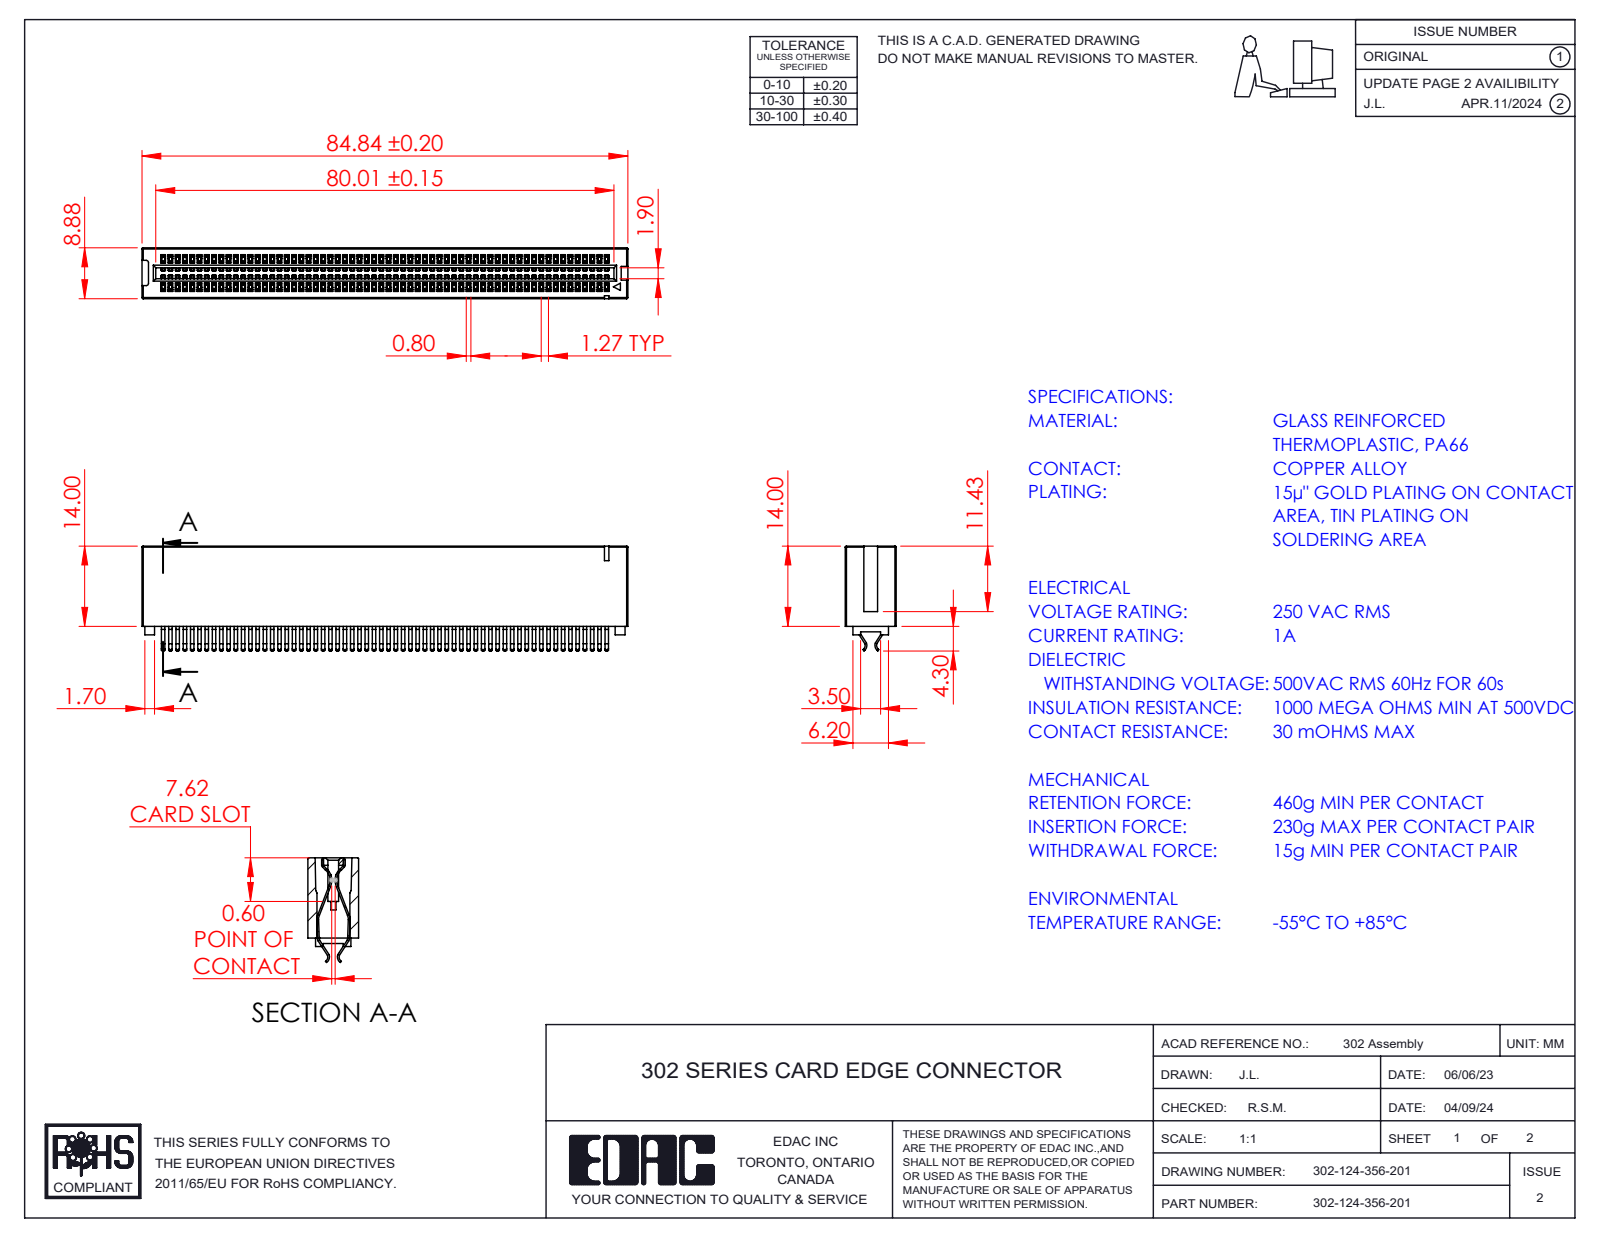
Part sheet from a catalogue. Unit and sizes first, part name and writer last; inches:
Units: inches
Overall size (bounding box): 3.34 × 0.72 × 0.35
Partial cylindrical surfaces — rounded edges, fillets, slot ends (radius × count): R0.008 ×380, R0.004 ×2, R0.016 ×2, R0.016 ×2, R0.037 ×2, R0.041 ×2, R0.048 ×2, R0.049 ×2
Main face-to-face distances: 0.35, 0.05, 0.1, 0.15, 0.031, 0.019, 0.075, 0.2, 0.137, 0.212
Volume: 0.394 in³ · Surface area: 29.01 in²
Bodies: 125 solids, 5956 faces (3955 planar, 1997 cylindrical, 4 other)
Part name (STEP PRODUCT): 302-124-356-201; Contact_302-290-X56; HSG_Vertical HSG
STEP written by: SolidWorks 2023 (CONFIG_CONTROL_DESIGN)
